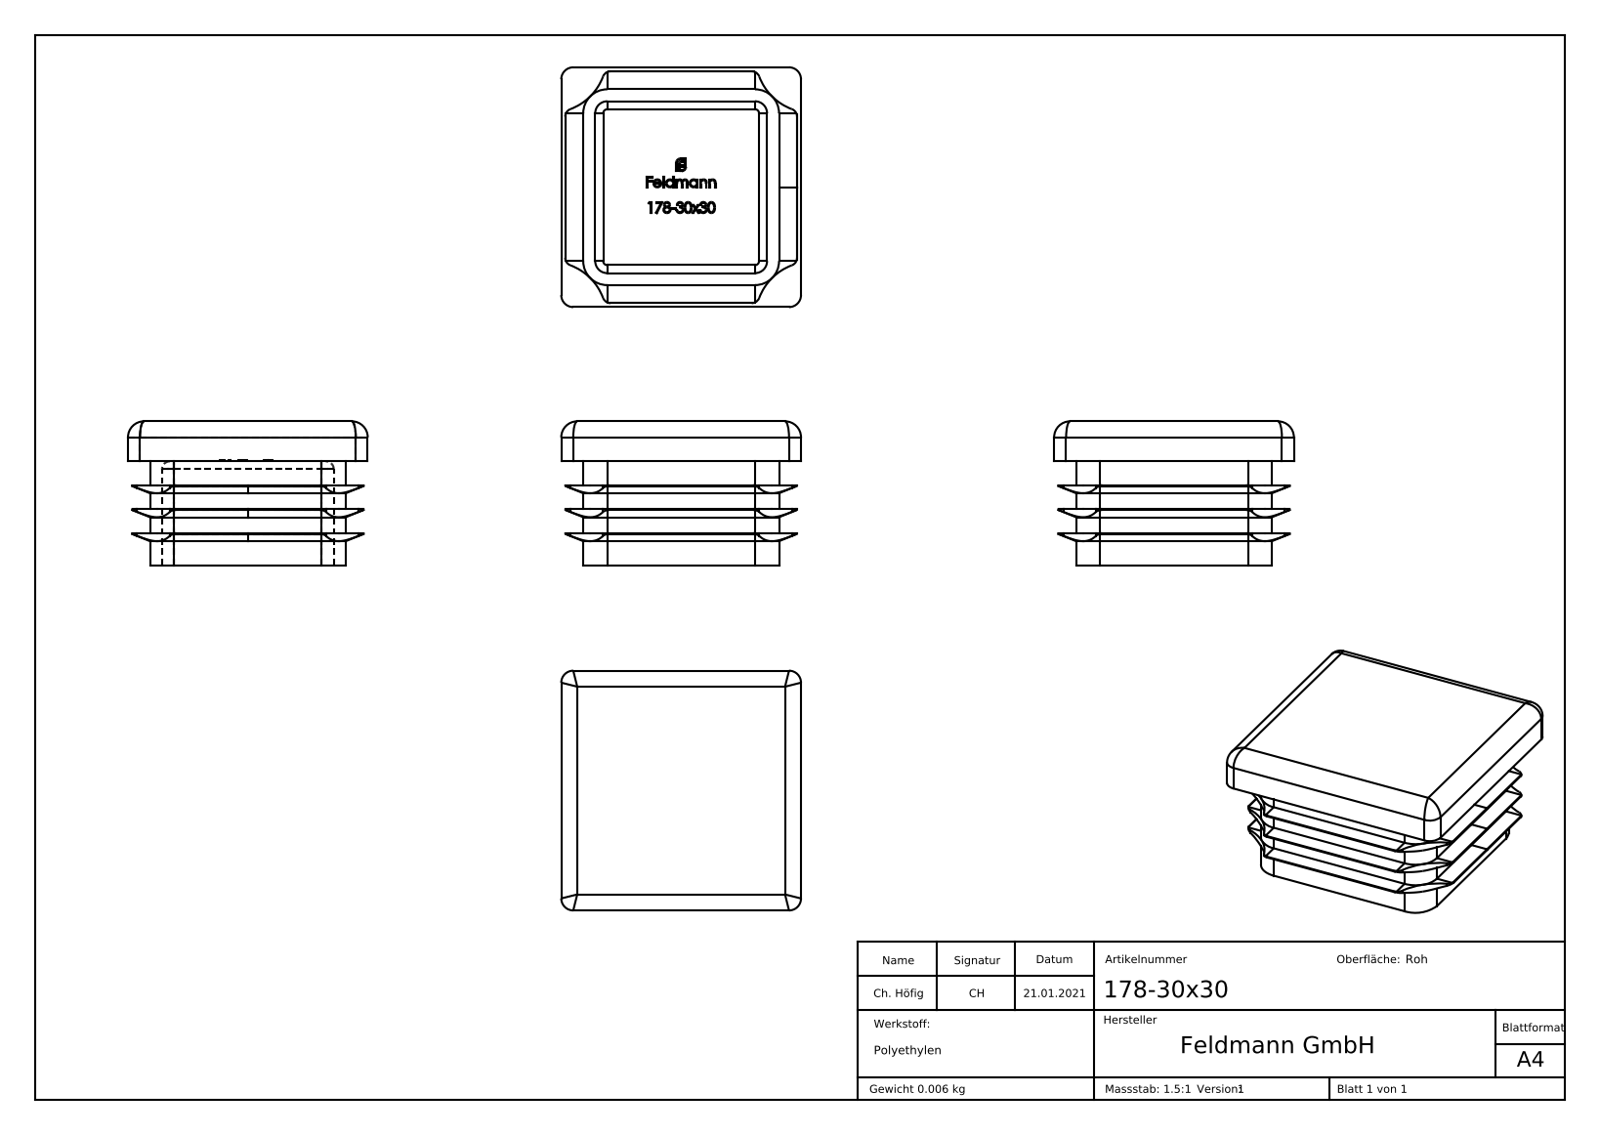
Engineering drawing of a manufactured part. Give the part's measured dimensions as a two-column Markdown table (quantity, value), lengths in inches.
| quantity | value |
| --- | --- |
| part name | 178-30x30 |
| STEP written by | SolidWorks 2018 (CONFIG_CONTROL_DESIGN) |
| units | inches |
| bodies | 1 solid, 465 faces (235 planar, 83 cylindrical, 147 other) |
| overall size | 1.181 × 1.181 × 0.709 |
| volume | 0.392 in³ |
| surface area | 8.479 in² |
| partial cylindrical surfaces (radius × count) | 0.039 × 12, 0.059 × 8, 0.079 × 4, 0.118 × 4, 0.276 × 4 |
| main face-to-face distances | 0.059, 0.906, 0.197, 0.118, 0.846, 0.965, 0.236, 0.109, 0.167, 0.108 |
